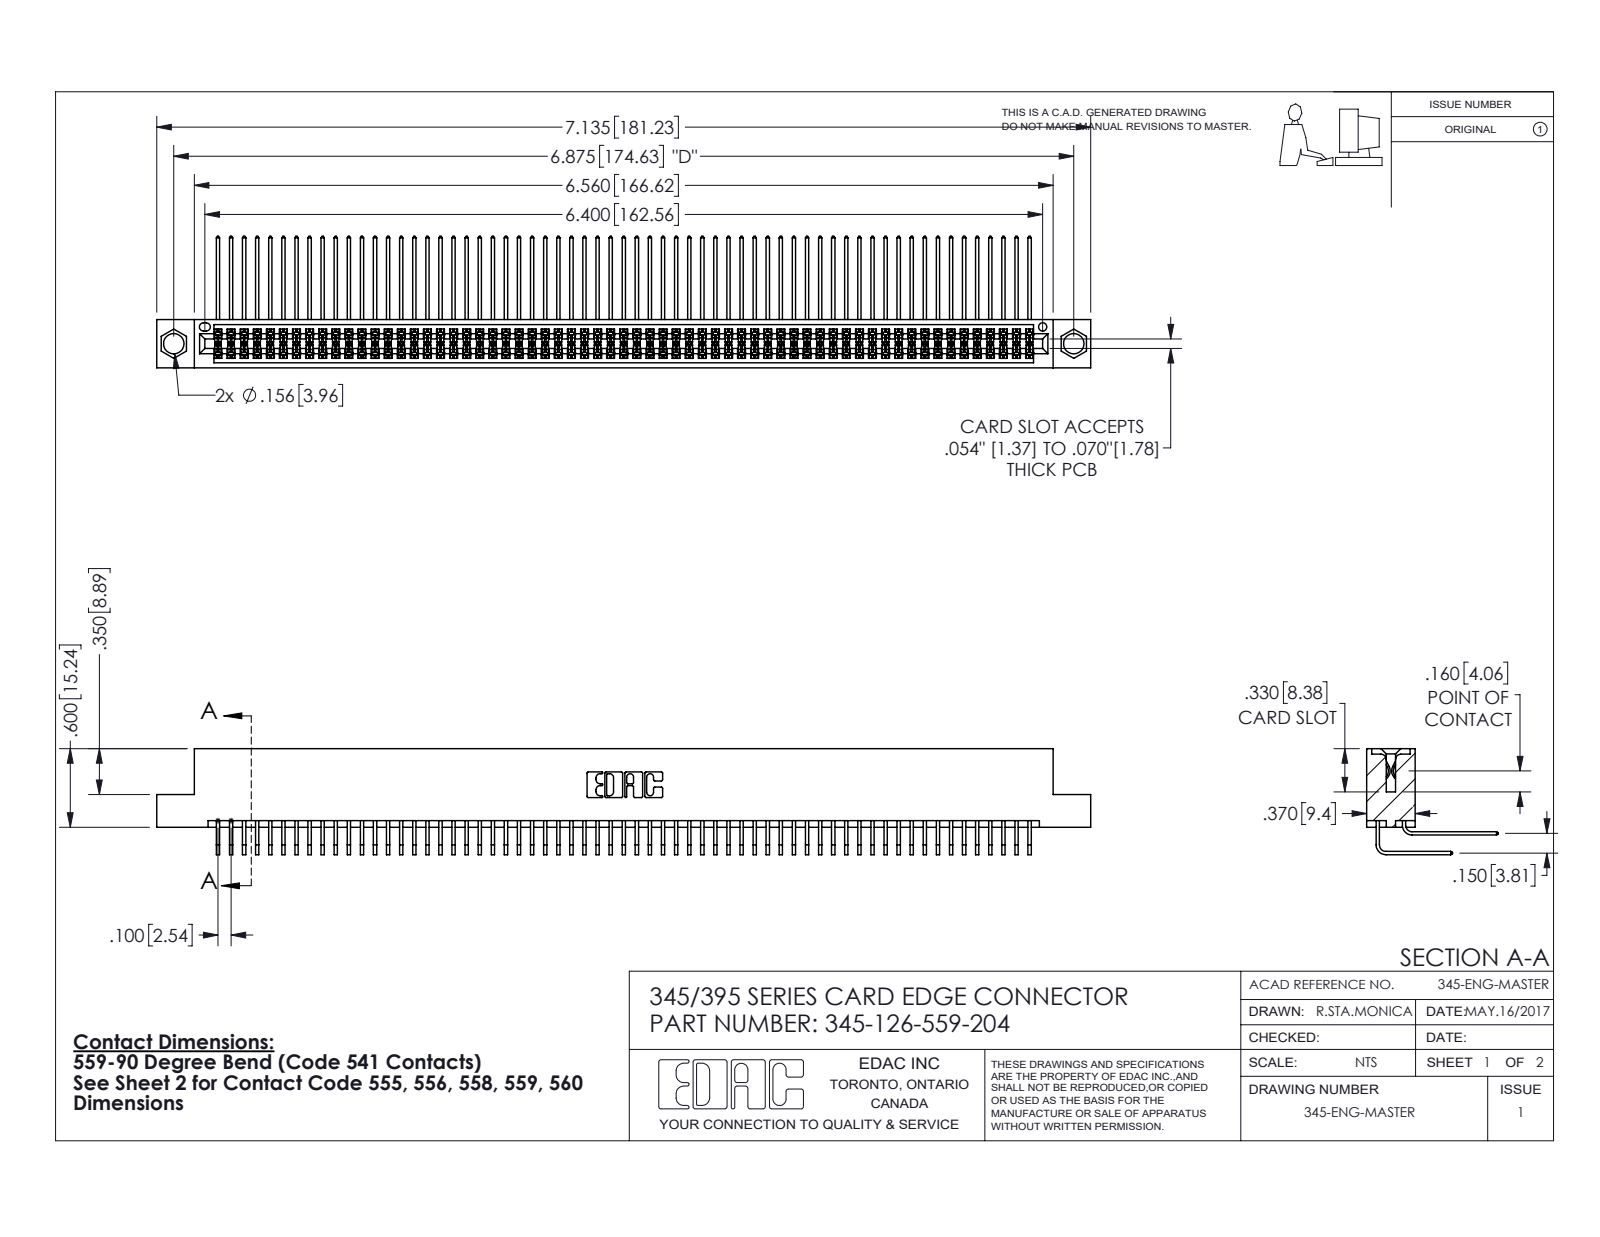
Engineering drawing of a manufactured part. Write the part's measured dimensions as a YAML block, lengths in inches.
part_name: "345-292-001_559 Tail - 2; 345 Part_Flush Mounting Lugs - 0.156 Dia-TI; 345-292-001_558 559 Tail - 1; 345-126-559-204"
step_written_by: "SolidWorks 2020 (CONFIG_CONTROL_DESIGN)"
units: inches
bodies: {solids: 127, faces: 6692, planar: 4504, cylindrical: 2188, other: 0}
overall_size: [7.135, 1.005, 0.809]
volume: 1.124
surface_area: 47.9
round_holes:
  - {diameter: 0.156, count: 2}
  - {diameter: 0.064, count: 1}
partial_cylinders:
  - {radius: 0.006, count: 189}
  - {radius: 0.01, count: 22}
  - {radius: 0.007, count: 6}
  - {radius: 0.031, count: 6}
  - {radius: 0.026, count: 3}
  - {radius: 0.014, count: 2}
  - {radius: 0.019, count: 2}
  - {radius: 0.022, count: 2}
face_to_face_distances: [0.072, 0.298, 0.2, 0.37, 0.098, 0.272, 0.025, 0.225, 0.175, 0.15]
hole_center_spacings: [0.27, 6.639, 6.875]
